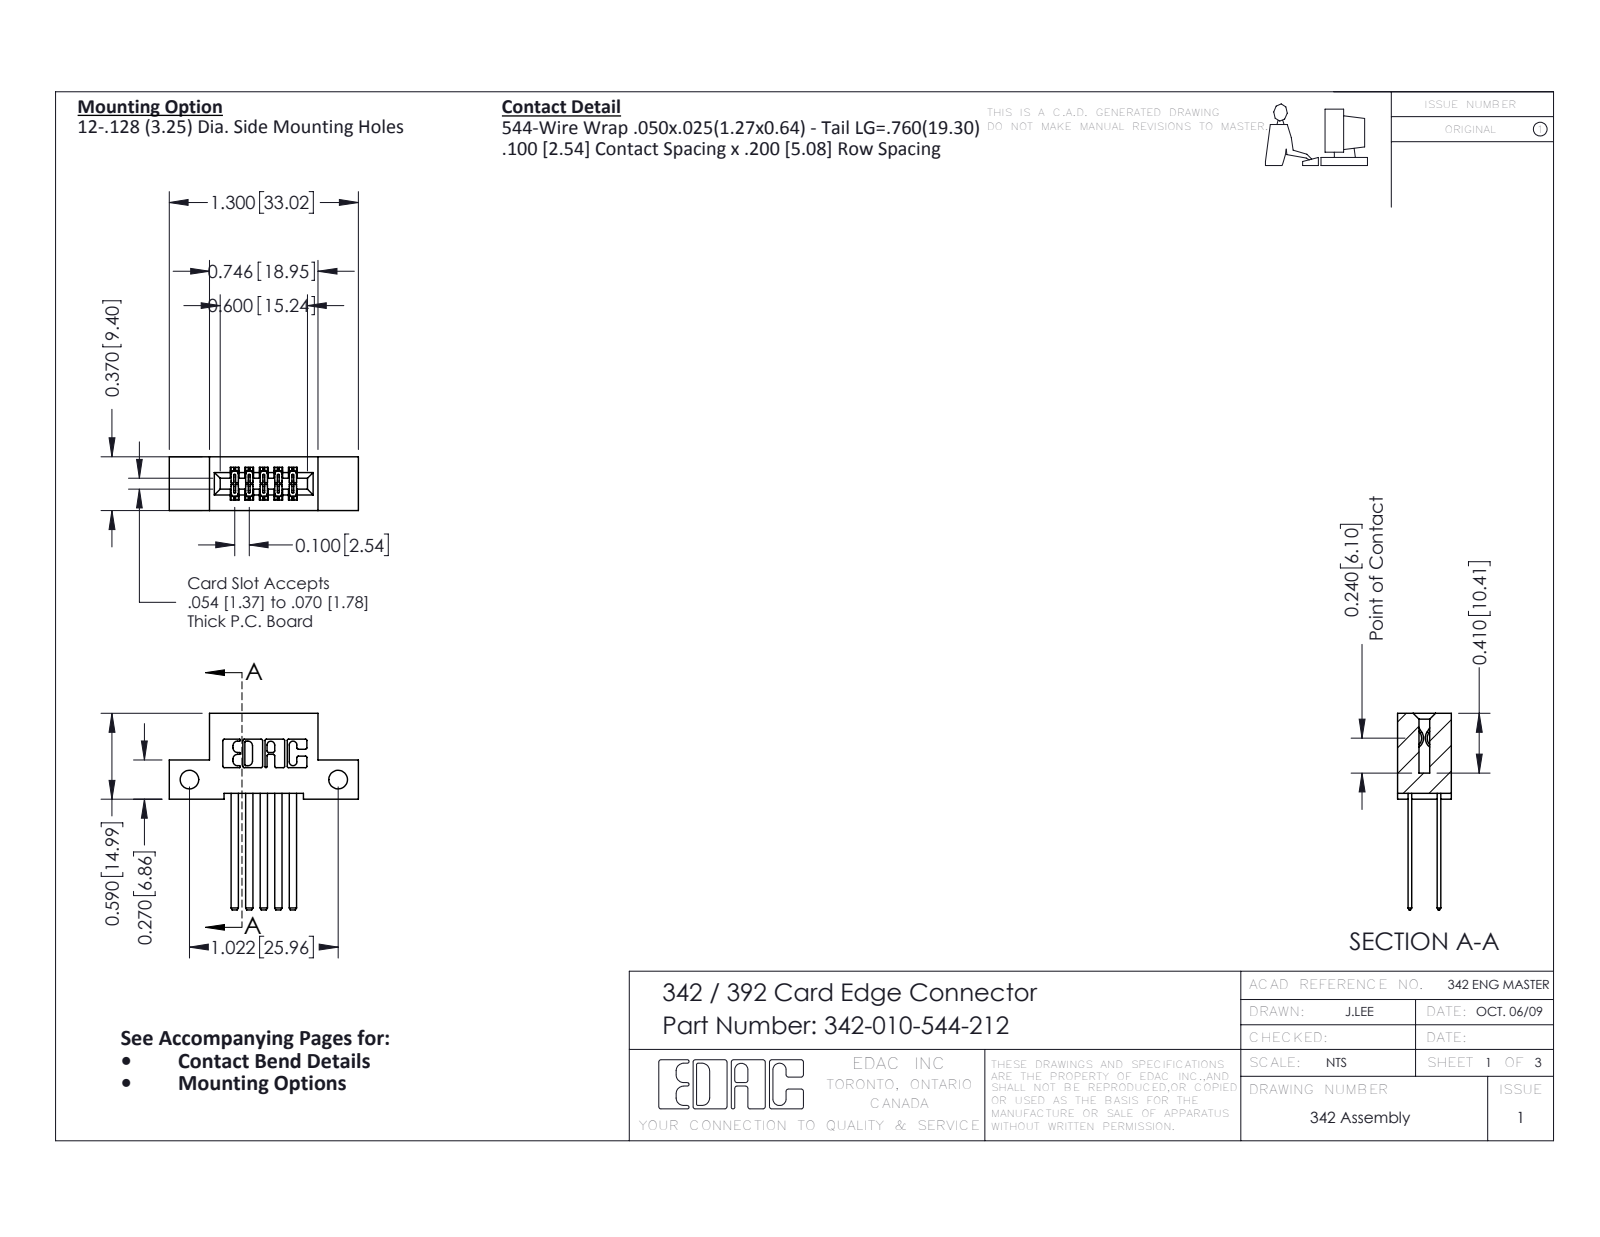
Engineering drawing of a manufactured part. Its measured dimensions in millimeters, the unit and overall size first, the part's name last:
Units: millimetres
Overall size (bounding box): 34.3 × 33 × 9.4
Round holes (diameter × count): ⌀3.3 ×2
Partial cylindrical surfaces — rounded edges, fillets, slot ends (radius × count): R0.3 ×22, R0.2 ×15, R0.2 ×6, R0.8 ×6, R0.7 ×3, R0.4 ×2, R0.6 ×2, R0.6 ×2
Main face-to-face distances: 5.1, 1.8, 7.6, 2.5, 2.5, 6.9, 0.6, 9.4, 1, 5.7
Hole centre spacings: 26
Volume: 2 850 mm³ · Surface area: 3 969 mm²
Bodies: 11 solids, 570 faces (386 planar, 184 cylindrical, 0 other)
Part name (STEP PRODUCT): 342-010-544-212; 342 Part_Side Mount; 345-292-001_345-293-144
STEP written by: SolidWorks 2016 (CONFIG_CONTROL_DESIGN)
